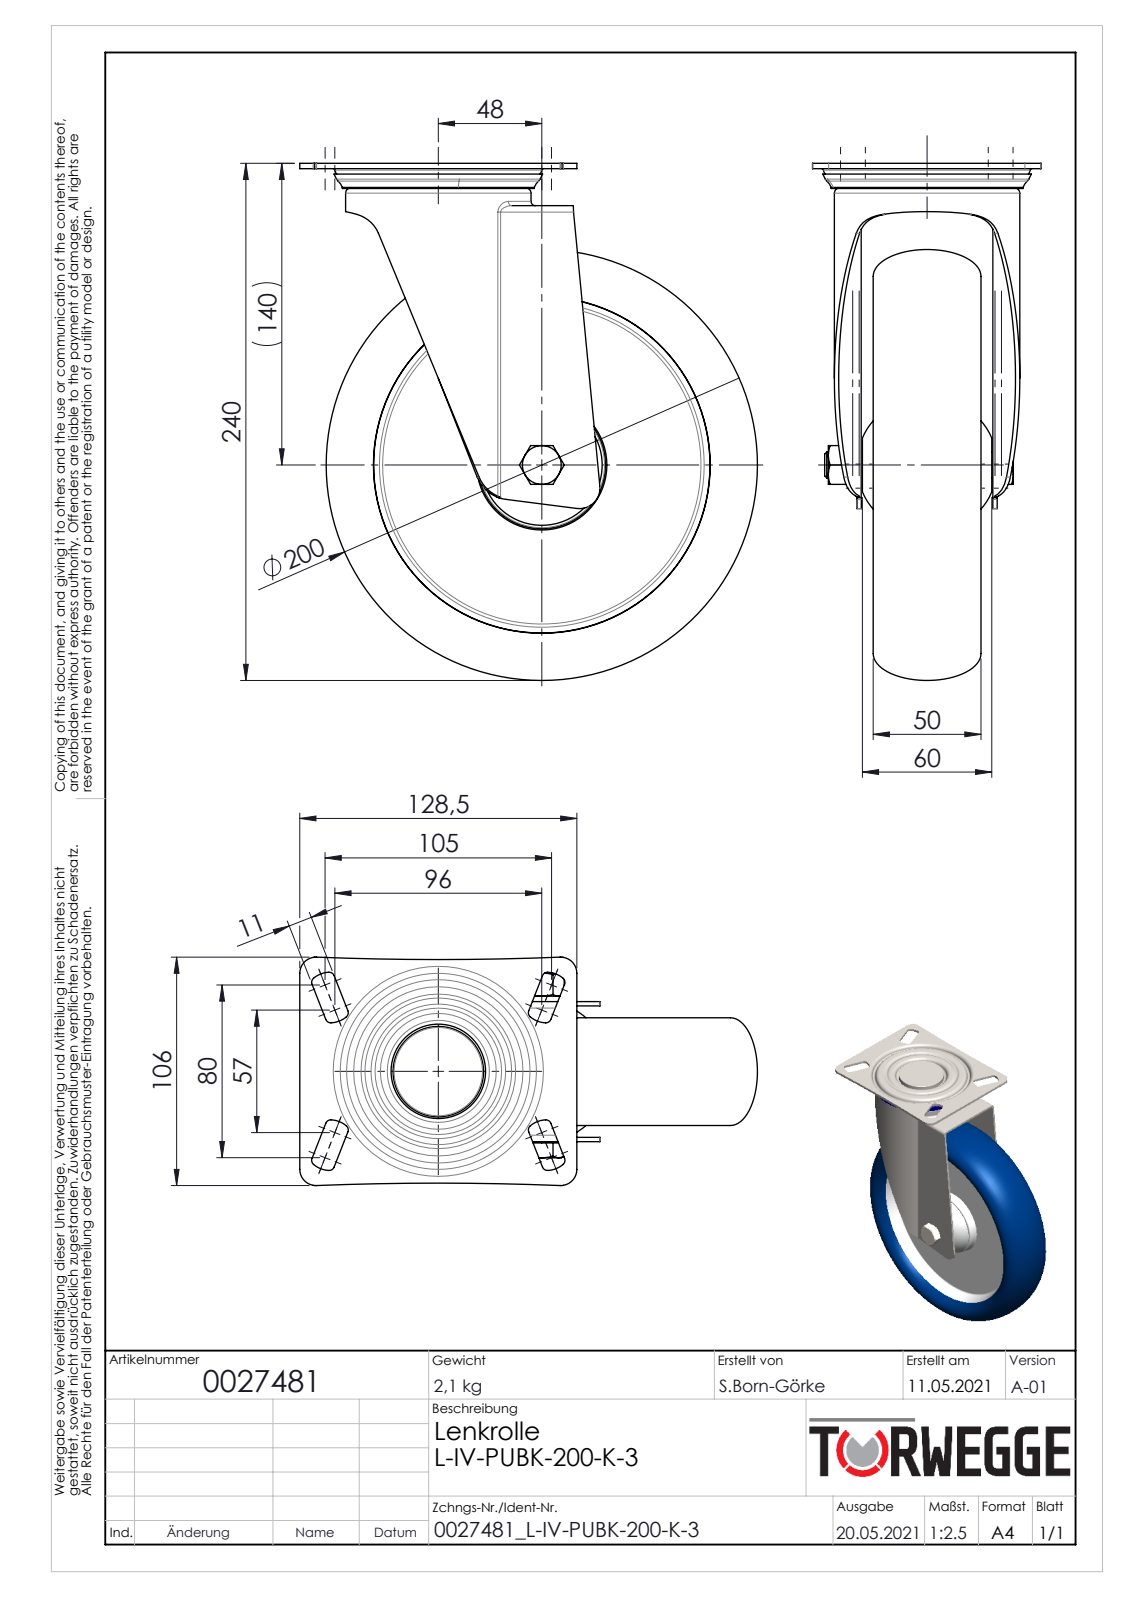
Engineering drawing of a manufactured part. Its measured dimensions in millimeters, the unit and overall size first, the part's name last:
Units: millimetres
Overall size (bounding box): 240 × 211.75 × 106
Round holes (diameter × count): ⌀10.2 ×1, ⌀12 ×1, ⌀12.2 ×1, ⌀12.3 ×1, ⌀34 ×1, ⌀38 ×1, ⌀44 ×1, ⌀47 ×1, ⌀50.5 ×1, ⌀54 ×1, ⌀82 ×1
Round bosses / shafts (diameter × count): ⌀89 ×1, ⌀86 ×1, ⌀54.5 ×1, ⌀42 ×1, ⌀41 ×1, ⌀38 ×1, ⌀20.2 ×1, ⌀20 ×1
Partial cylindrical surfaces — rounded edges, fillets, slot ends (radius × count): R2.5 ×16, R1 ×4, R7.5 ×4, R11.75 ×4, R2 ×2, R3 ×2, R1424.42 ×2, R9.5 ×1
Main face-to-face distances: 2, 11, 27, 38, 25, 36, 63, 2.5, 65, 61
Volume: 920 378 mm³ · Surface area: 296 100 mm²
Bodies: 11 solids, 453 faces (93 planar, 103 cylindrical, 257 other)
Part name (STEP PRODUCT): 0027481
STEP written by: SolidWorks 2020 (AUTOMOTIVE_DESIGN)
